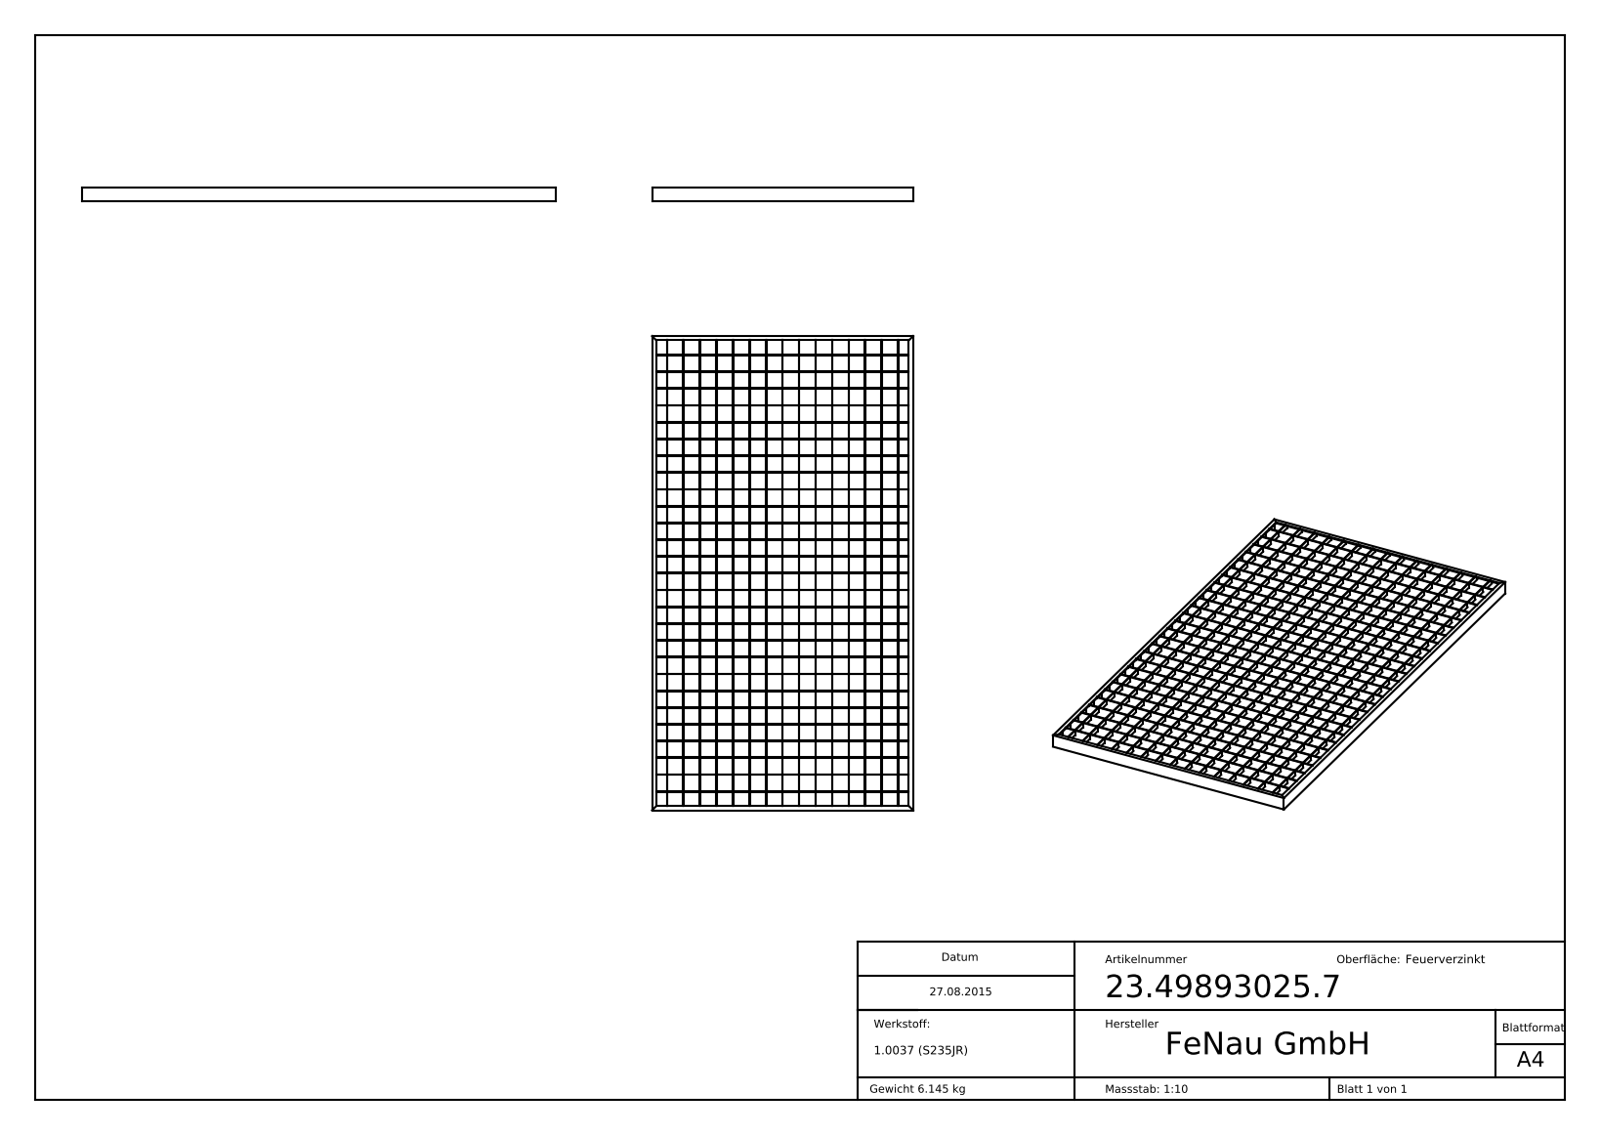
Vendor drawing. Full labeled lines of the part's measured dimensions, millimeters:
Part name (STEP PRODUCT): 23-49893025-7
STEP written by: SolidWorks 2015 (CONFIG_CONTROL_DESIGN)
Units: millimetres
Bodies: 1 solid, 1556 faces (1556 planar, 0 cylindrical, 0 other)
Overall size (bounding box): 890 × 490 × 25
Volume: 787 808 mm³ · Surface area: 1 142 000 mm²
Main face-to-face distances: 63, 31.5, 94.5, 126, 31, 157.5, 189, 62, 220.5, 252
